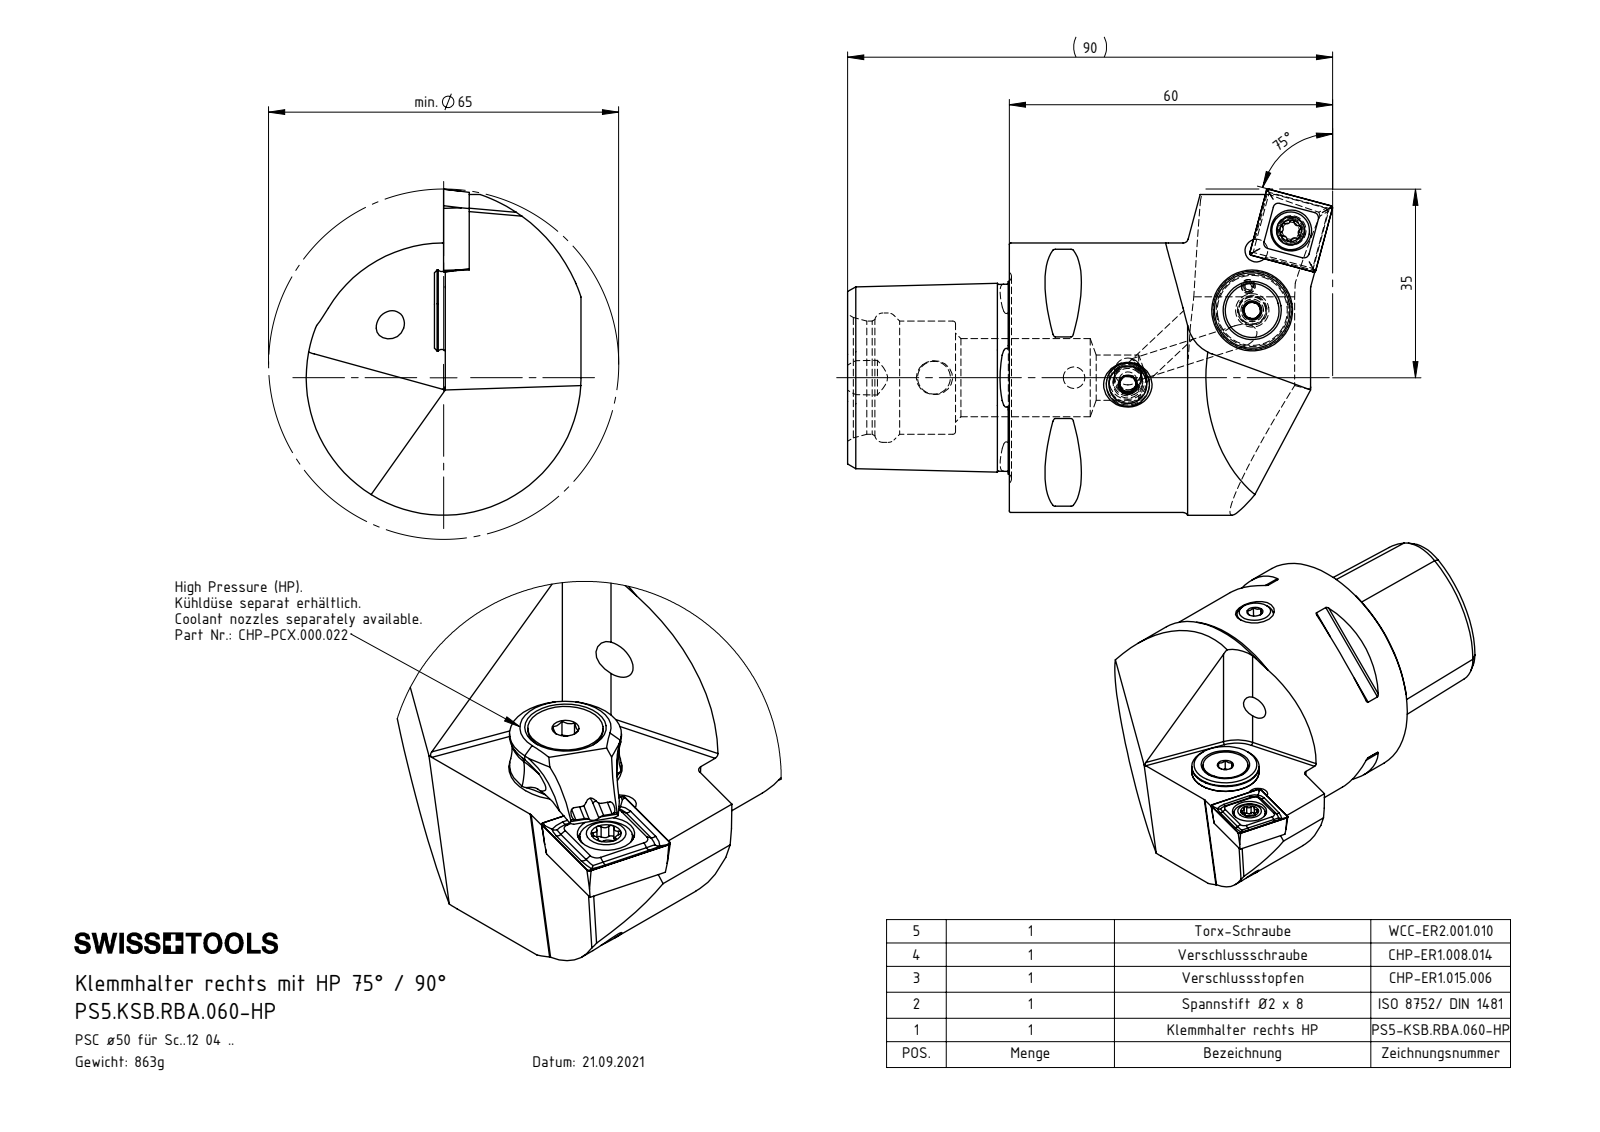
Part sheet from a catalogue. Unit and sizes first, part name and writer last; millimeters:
Units: millimetres
Overall size (bounding box): 90 × 60.5 × 51
Round holes (diameter × count): ⌀4.2 ×4, ⌀5 ×2, ⌀1.2 ×1, ⌀2 ×1, ⌀3 ×1, ⌀4 ×1, ⌀5.3 ×1, ⌀5.5 ×1, ⌀6.1 ×1, ⌀7 ×1, ⌀7.6 ×1, ⌀8.4 ×1
Round bosses / shafts (diameter × count): ⌀5 ×2, ⌀50 ×1, ⌀14.85 ×1, ⌀13.4 ×1, ⌀10 ×1, ⌀8 ×1, ⌀7 ×1, ⌀5.5 ×1
Partial cylindrical surfaces — rounded edges, fillets, slot ends (radius × count): R0.5 ×12, R1 ×7, R0.39 ×6, R0.69 ×6, R6 ×3, R1.1 ×2, R1.2 ×2, R5 ×2
Main face-to-face distances: 30, 25.2, 20.74, 4.46, 19.18, 20.7, 4.5, 44.4, 1.5, 3
Hole centre spacings: 4.5, 6.83, 7.36, 7.45, 11.13, 13.01, 13.09, 16.42
Volume: 109 717 mm³ · Surface area: 23 837 mm²
Bodies: 9 solids, 478 faces (102 planar, 135 cylindrical, 241 other)
Part name (STEP PRODUCT): CHP-PCX.000.022_Düse; SCMT120404; PS5.KSB.RBA.060-HP; DIN 7991 - M5x18 (+7 more)
STEP written by: SolidWorks 2022 (CONFIG_CONTROL_DESIGN)
